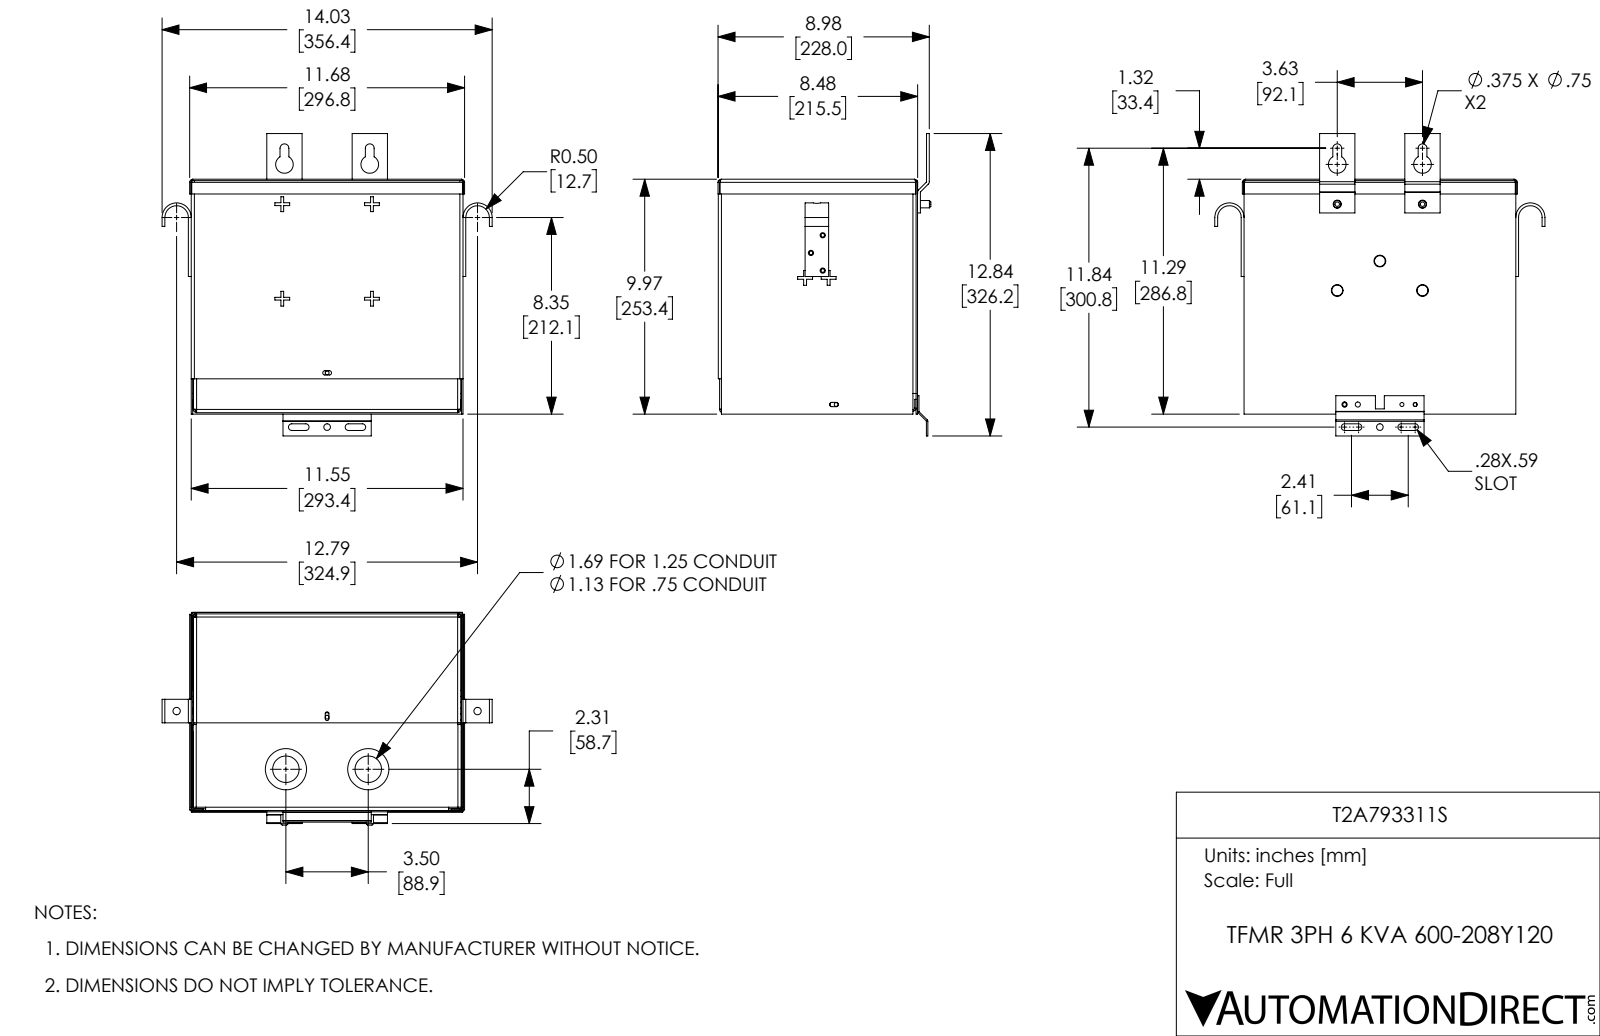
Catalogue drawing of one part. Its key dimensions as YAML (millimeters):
part_name: "T2A793311S"
step_written_by: "SolidWorks 2017 (AUTOMOTIVE_DESIGN)"
units: millimeters
bodies: {solids: 12, faces: 602, planar: 392, cylindrical: 138, other: 72}
overall_size: [356.4, 326.2, 229.7]
volume: 668800
surface_area: 869700
round_holes:
  - {diameter: 4.1, count: 5}
  - {diameter: 4.4, count: 2}
  - {diameter: 5.6, count: 2}
  - {diameter: 7.1, count: 2}
  - {diameter: 8, count: 2}
  - {diameter: 8.7, count: 2}
  - {diameter: 19.1, count: 2}
  - {diameter: 44.5, count: 2}
  - {diameter: 4.4, count: 1}
  - {diameter: 4.7, count: 1}
  - {diameter: 28.6, count: 1}
  - {diameter: 28.6, count: 1}
round_bosses_or_shafts:
  - {diameter: 47.5, count: 2}
  - {diameter: 31.6, count: 2}
  - {diameter: 7.9, count: 2}
partial_cylinders:
  - {radius: 1.9, count: 16}
  - {radius: 3.4, count: 16}
  - {radius: 2.4, count: 8}
  - {radius: 3.6, count: 4}
  - {radius: 0.5, count: 2}
  - {radius: 0.8, count: 2}
  - {radius: 2, count: 2}
  - {radius: 2, count: 2}
face_to_face_distances: [1.5, 213.6, 212.1, 250.3, 215.1, 1.5, 291.9, 1.7, 248.7, 293.4]
hole_center_spacings: [14.3, 34.1, 41.6, 42.8, 45.2, 51.2, 61.9, 71.7]
